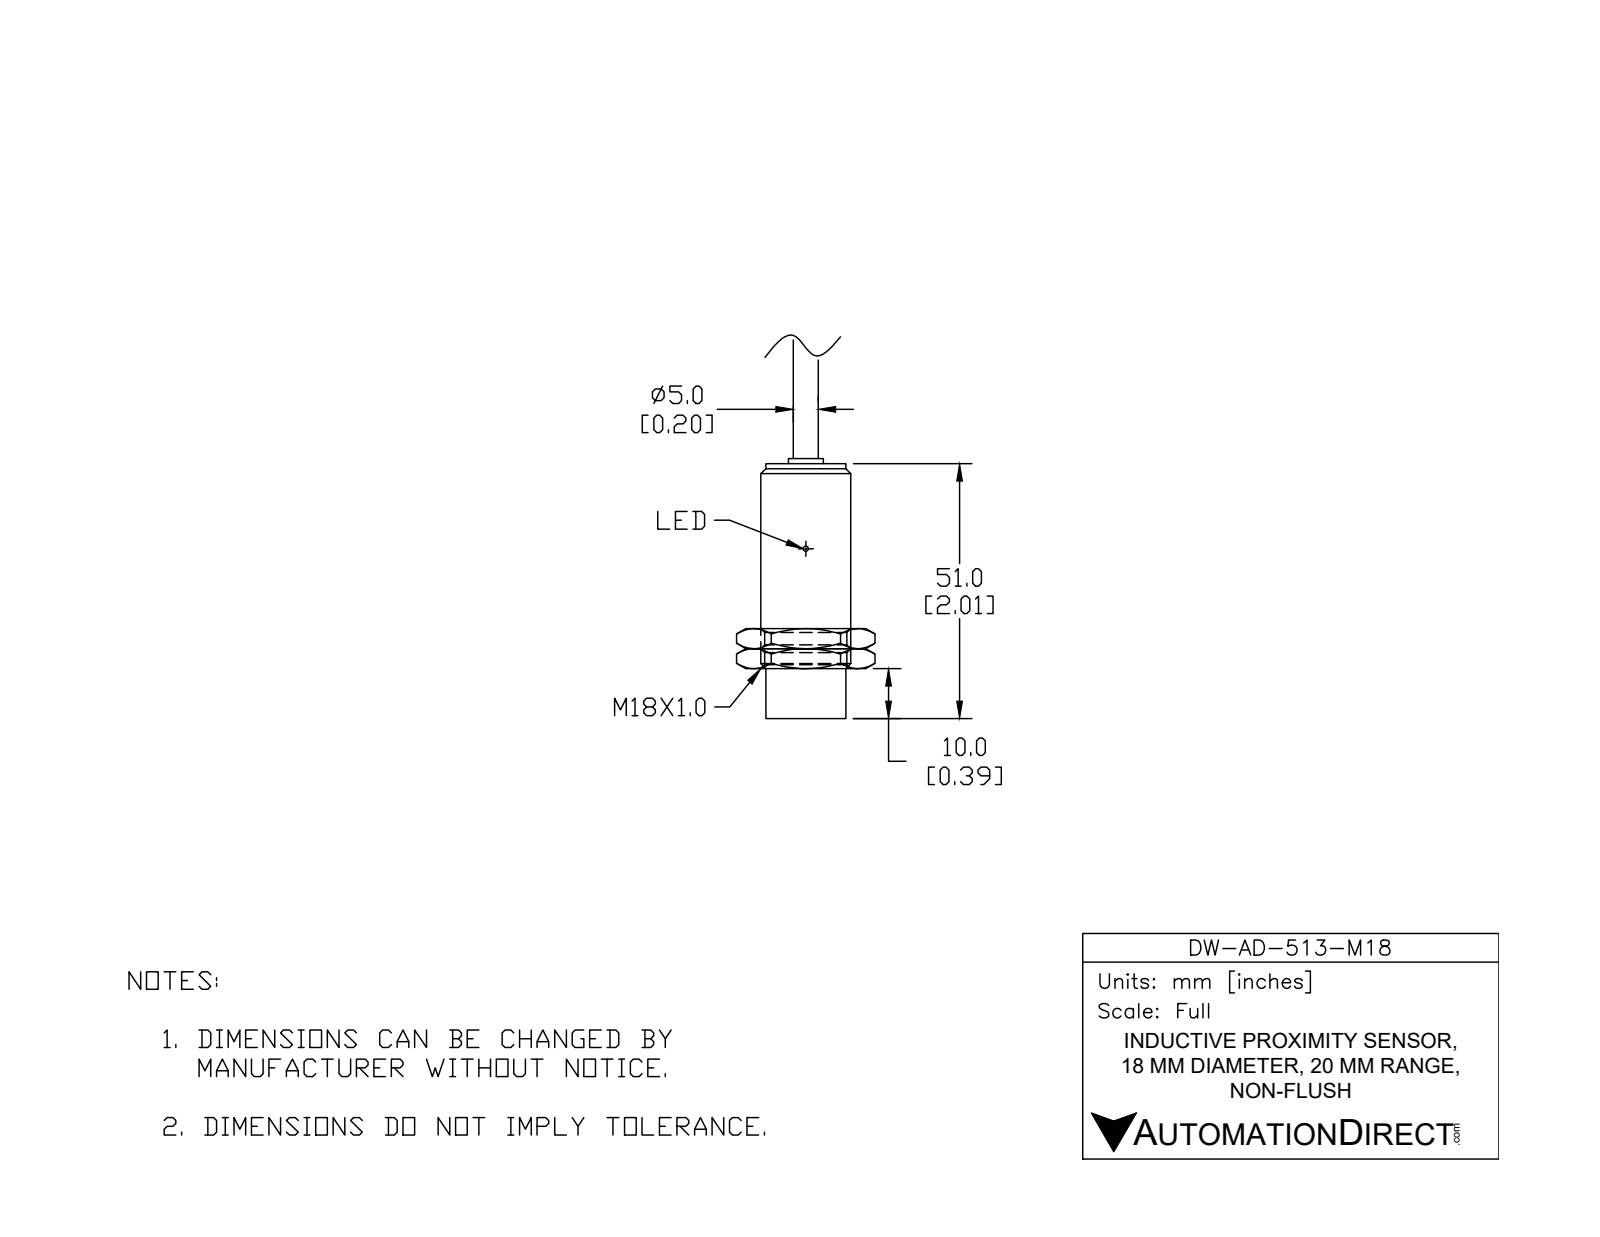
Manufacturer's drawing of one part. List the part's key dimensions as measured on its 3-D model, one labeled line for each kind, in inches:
Part name (STEP PRODUCT): DW-AD-513-M18
STEP written by: SolidWorks 2017 (AUTOMOTIVE_DESIGN)
Units: inches
Bodies: 2 solids, 37 faces (18 planar, 7 cylindrical, 12 other)
Overall size (bounding box): 3.016 × 0.709 × 0.709
Volume: 0.804 in³ · Surface area: 5.913 in²
Round bosses / shafts (diameter × count): ⌀0.709 ×1, ⌀0.65 ×1, ⌀0.646 ×1, ⌀0.413 ×1, ⌀0.268 ×1, ⌀0.197 ×1, ⌀0.118 ×1
Main face-to-face distances: 2.008, 0.031, 2.087, 0.079, 2.039, 0.047, 1.89, 0.118, 0.15, 0.197
